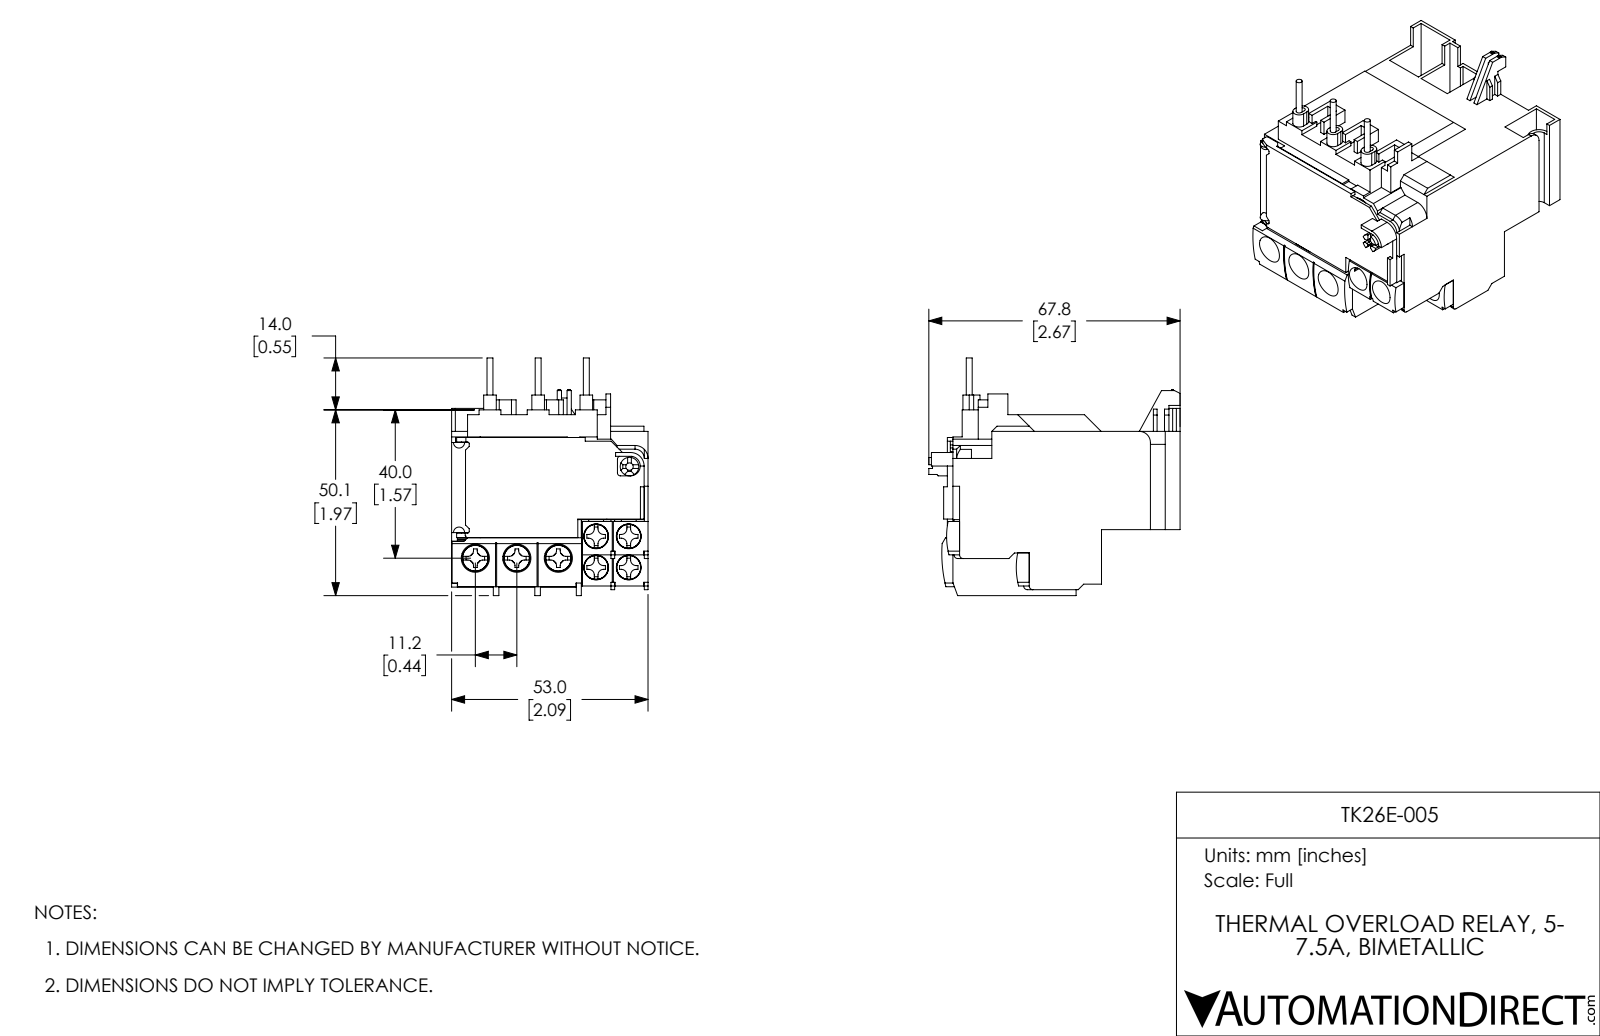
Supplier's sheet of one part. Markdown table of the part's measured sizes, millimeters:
| quantity | value |
| --- | --- |
| part name | TK26E-005 |
| STEP written by | SolidWorks 2017 (AUTOMOTIVE_DESIGN) |
| units | millimeters |
| bodies | 38 solids, 1480 faces (1225 planar, 220 cylindrical, 35 other) |
| overall size | 67.8 × 64.1 × 53 |
| volume | 99 940 mm³ |
| surface area | 38 810 mm² |
| round holes (diameter × count) | 3.5 × 4, 3.6 × 4, 6.7 × 4, 4 × 3, 4.1 × 3, 7.6 × 3, 1 × 1, 2 × 1, 5 × 1, 11 × 1 |
| round bosses / shafts (diameter × count) | 6.6 × 4, 1.6 × 3, 6 × 1 |
| partial cylindrical surfaces (radius × count) | 1.5 × 28, 1 × 8, 0.5 × 6, 1.7 × 6, 0.8 × 5, 1.2 × 4, 4.3 × 4, 4.8 × 3 |
| main face-to-face distances | 1, 9, 1.5, 12, 53, 2, 10, 11, 8.7, 0.7 |
| hole center spacings | 8.4, 8.8, 11.2, 12.2, 9.6, 10.5, 11.8, 18.8 |
